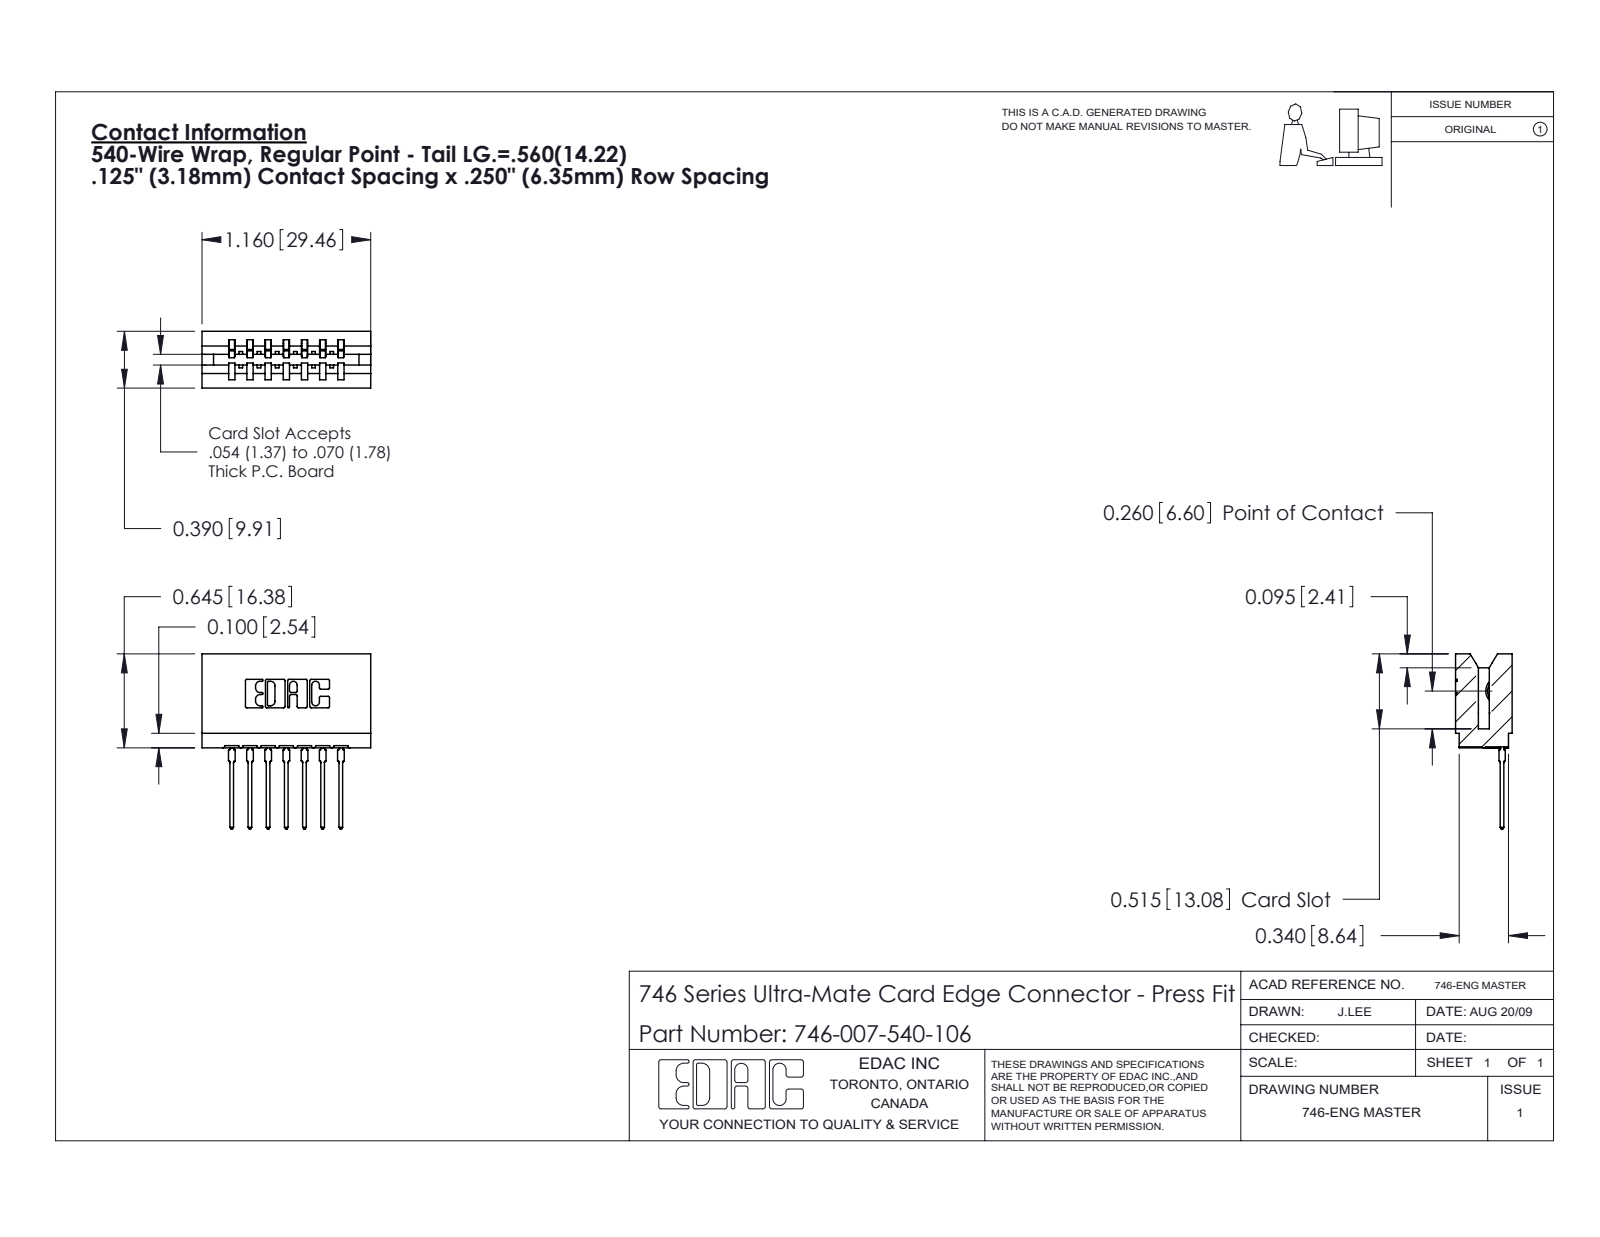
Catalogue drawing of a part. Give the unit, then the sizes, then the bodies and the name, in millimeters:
Units: millimetres
Overall size (bounding box): 30.6 × 29.5 × 9.9
Partial cylindrical surfaces — rounded edges, fillets, slot ends (radius × count): R0.3 ×22, R0.5 ×14, R0.4 ×8, R0.2 ×6, R0.8 ×6, R0.1 ×4, R0.3 ×4, R0.7 ×3
Main face-to-face distances: 6.4, 1.1, 8.5, 12.7, 3.2, 3.2, 1.4, 5.3, 7.4, 9.9
Volume: 3 310 mm³ · Surface area: 4 418 mm²
Bodies: 8 solids, 854 faces (497 planar, 175 cylindrical, 182 other)
Part name (STEP PRODUCT): 746-007-540-106; 746 Part_.515 Slot Depth - 06; 746-292-001_540
STEP written by: SolidWorks 2020 (CONFIG_CONTROL_DESIGN)
